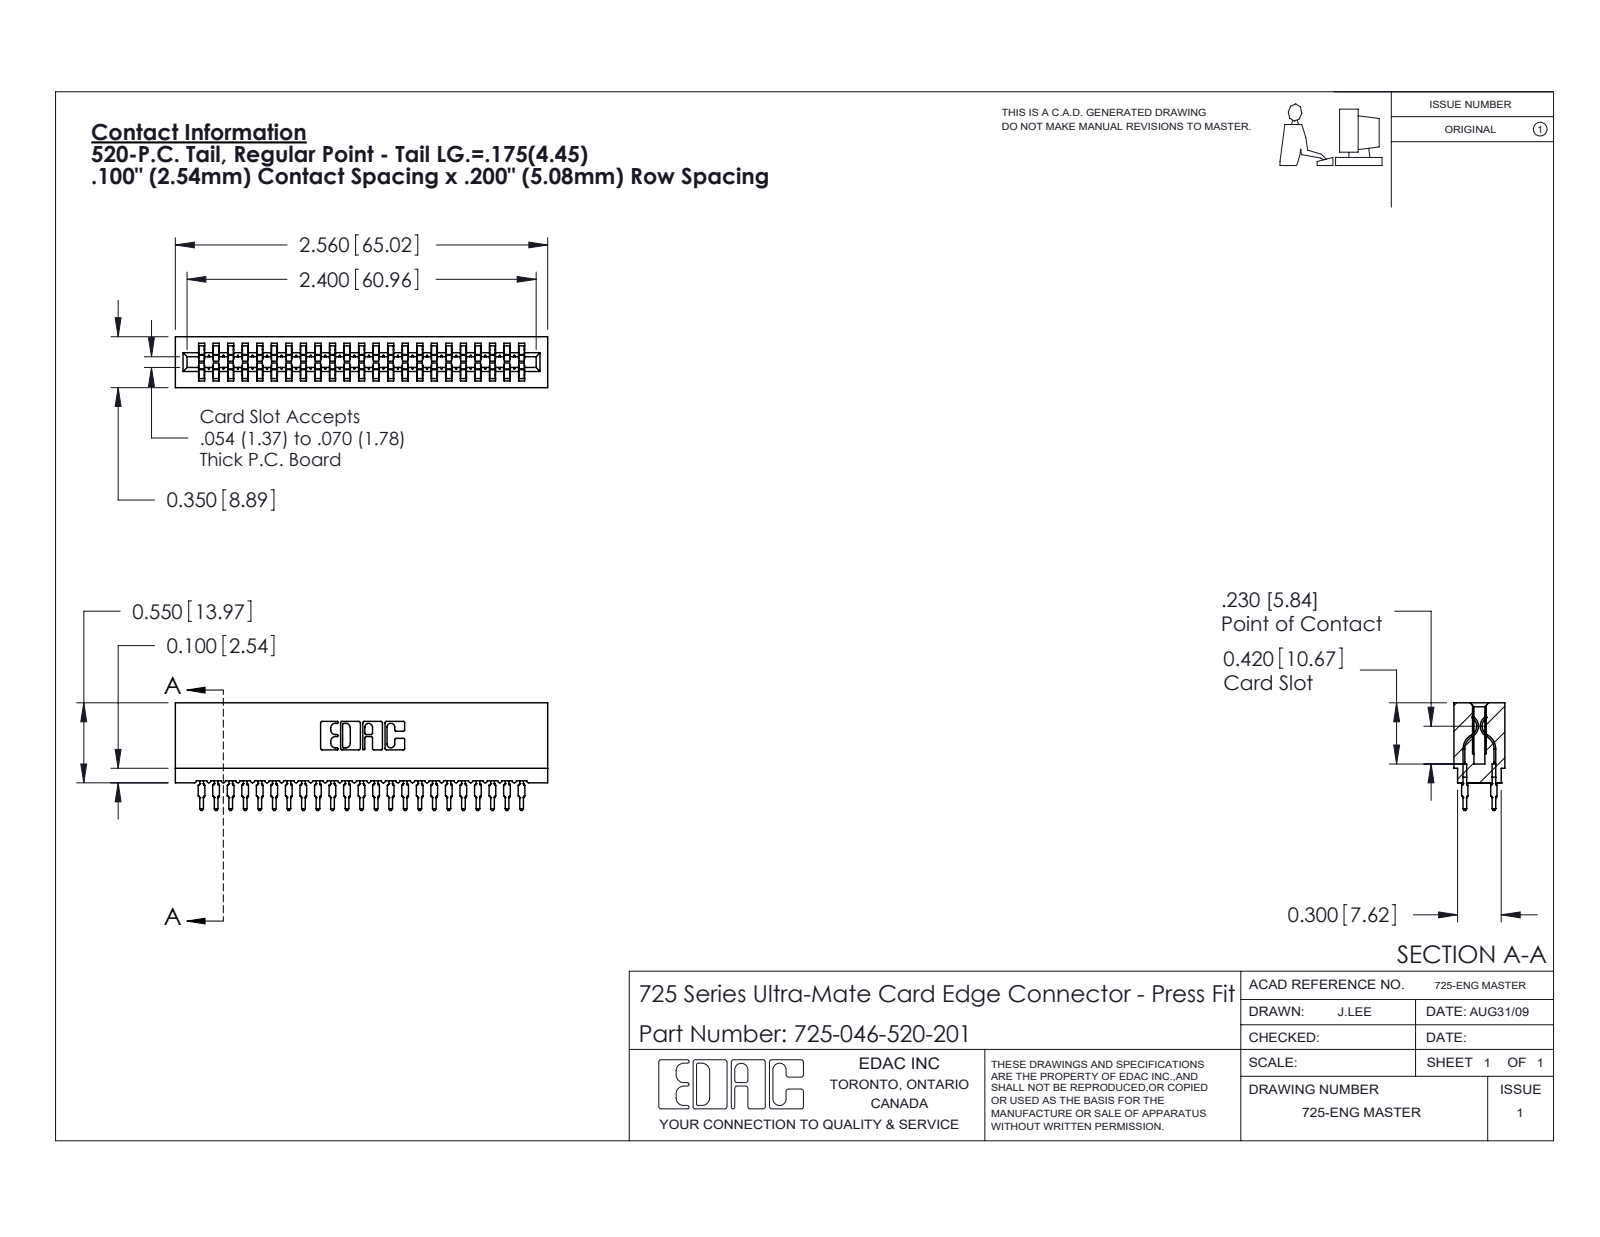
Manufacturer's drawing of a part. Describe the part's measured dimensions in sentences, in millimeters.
The part is named "725 Part_Insulator Option - 01; 745-292-001_520; 725-046-520-201". Its 3-D file was written by "SolidWorks 2020 (CONFIG_CONTROL_DESIGN)". It is 47 solids with 4212 faces: 2171 planar, 845 cylindrical and 1196 other. Overall it measures 65 by 18.8 by 8.9 millimeters. Its volume is 5 210 cubic millimeters and its surface area 10 410 square millimeters. Partial cylindrical surfaces (rounded edges, fillets, slot ends): 92 of radius 0.5, 46 of radius 0.4, 22 of radius 0.3, 8 of radius 0.1, 8 of radius 0.3, 6 of radius 0.2, 6 of radius 0.8, 3 of radius 0.7. The main face-to-face distances are 5.1, 2.5, 7.6, 10.2, 12.7, 15.2, 8.9, 17.8, 1.6, 7.3.
